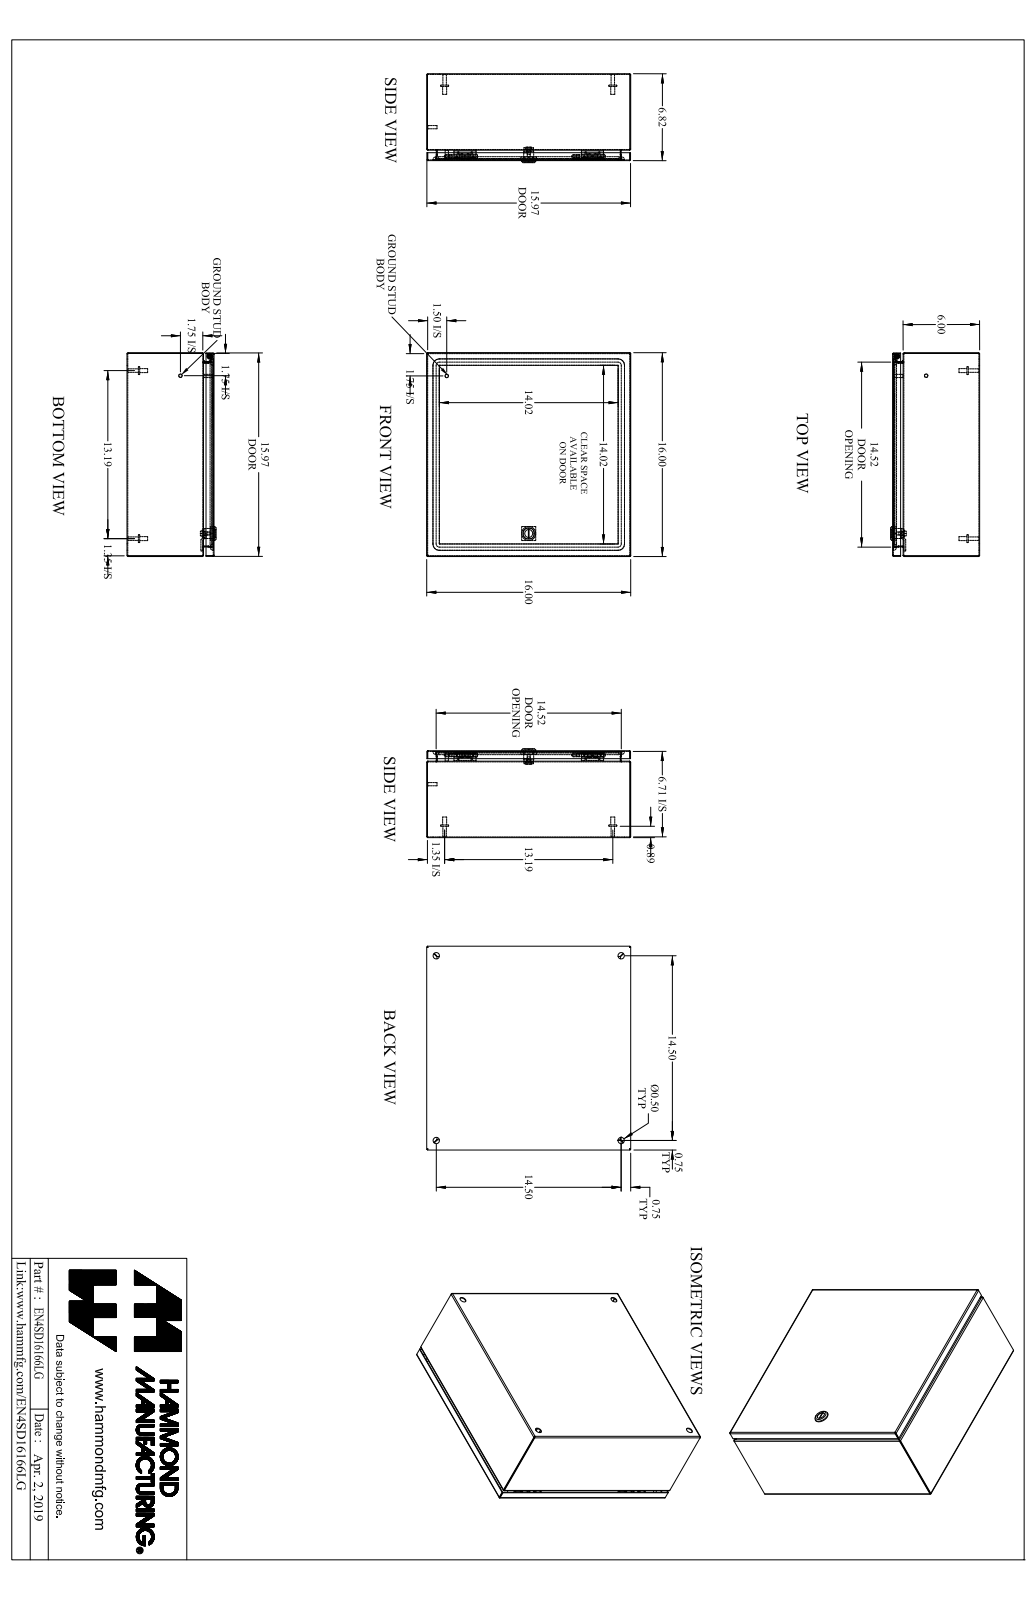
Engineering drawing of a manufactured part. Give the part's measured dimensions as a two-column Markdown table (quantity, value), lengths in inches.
| quantity | value |
| --- | --- |
| part name | EN4SD16166LG_Default |
| STEP written by | SolidWorks 2019 (CONFIG_CONTROL_DESIGN) |
| units | inches |
| bodies | 21 solids, 634 faces (285 planar, 213 cylindrical, 136 other) |
| overall size | 16 × 16 × 6.982 |
| volume | 64.65 in³ |
| surface area | 2 185 in² |
| round holes (diameter × count) | 0.5 × 4, 0.172 × 1, 0.232 × 1, 0.24 × 1, 0.242 × 1, 0.625 × 1, 0.785 × 1 |
| round bosses / shafts (diameter × count) | 0.625 × 4, 0.313 × 4, 0.27 × 4, 0.281 × 2, 0.25 × 2, 1.1 × 1, 0.525 × 1, 0.455 × 1 |
| partial cylindrical surfaces (radius × count) | 0.029 × 21, 0.086 × 21, 0.25 × 16, 19 × 8, 0.006 × 4, 0.062 × 4, 0.499 × 4, 0.125 × 2 |
| main face-to-face distances | 0.057, 6.765, 15.943, 6.708, 6.822, 15.886, 16, 0.822, 5.943, 0.749 |
| hole center spacings | 14.5, 20.506, 7.326, 7.327, 15.271, 15.272 |
